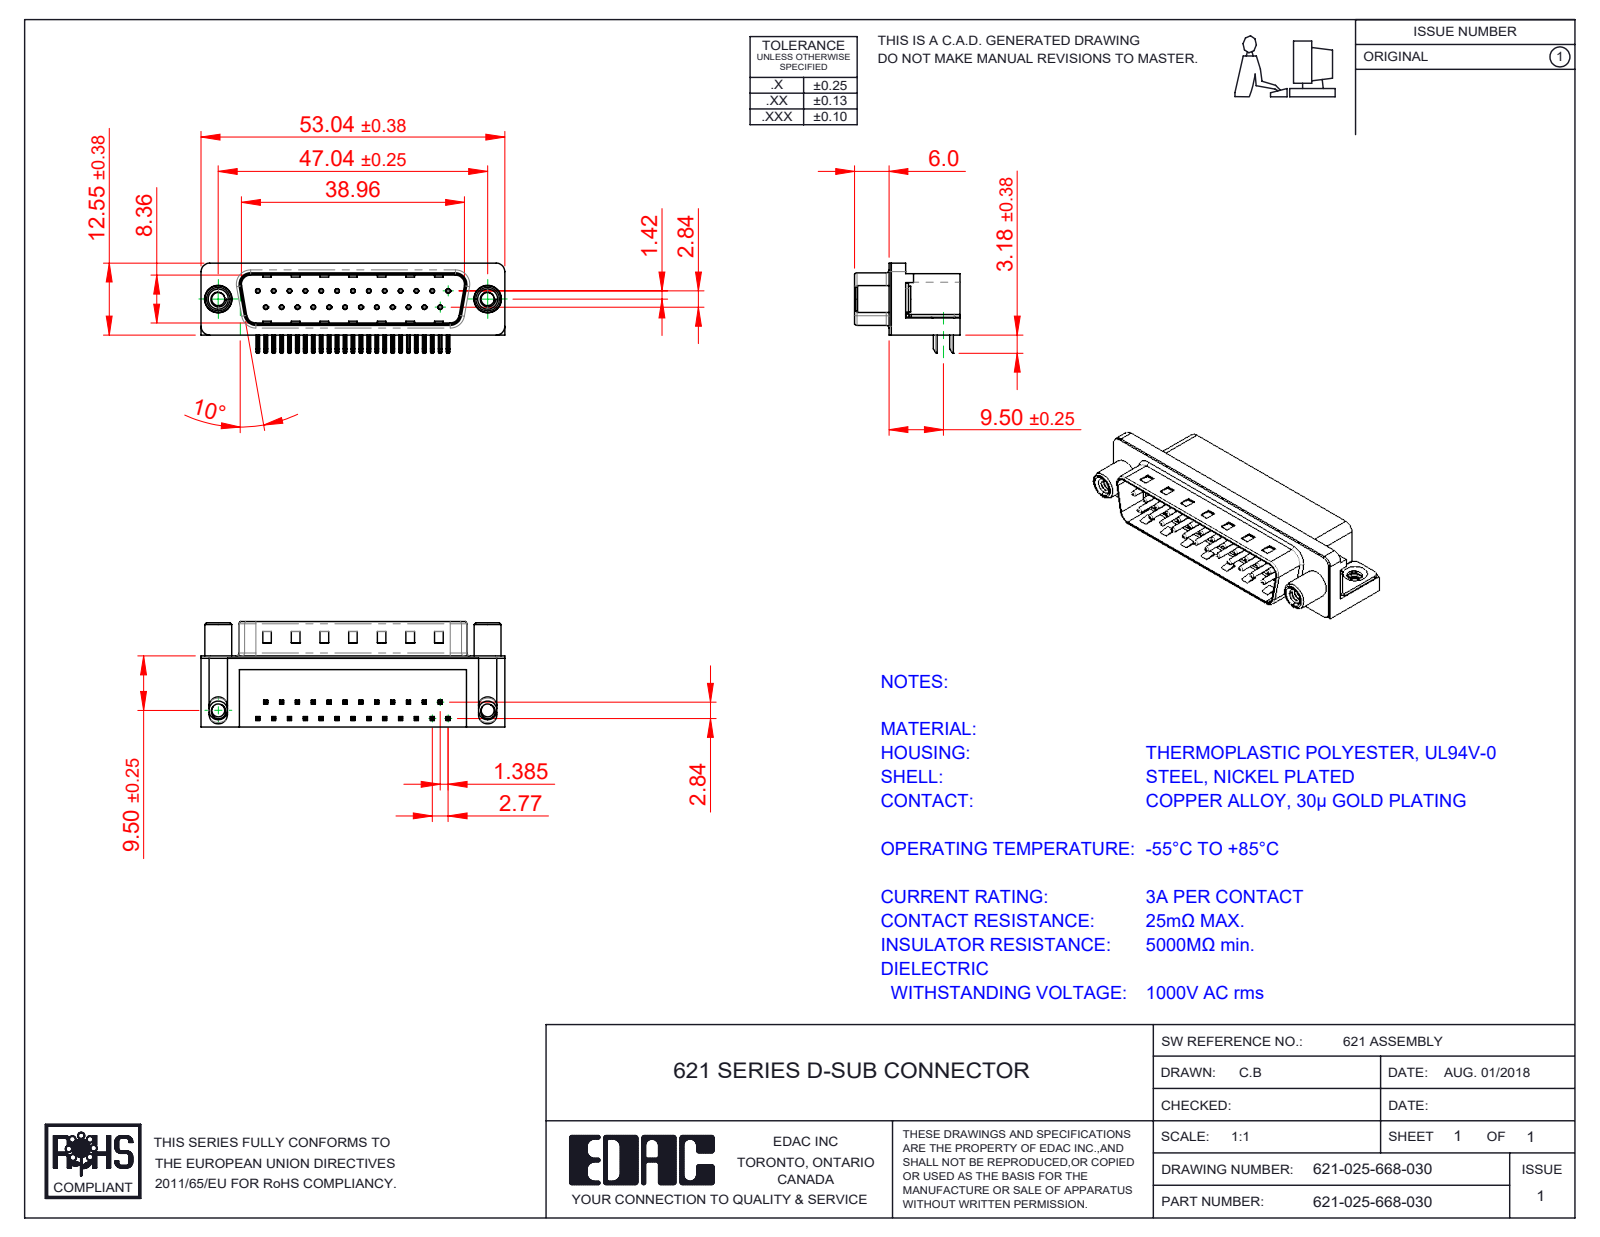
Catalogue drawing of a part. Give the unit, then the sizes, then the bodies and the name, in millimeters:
Units: millimetres
Overall size (bounding box): 53.04 × 18.4 × 16.25
Round holes (diameter × count): ⌀0.35 ×25, ⌀0.8 ×25, ⌀2.3 ×2, ⌀3.1 ×2, ⌀4 ×2, ⌀4.8 ×2, ⌀5 ×2
Round bosses / shafts (diameter × count): ⌀0.75 ×25, ⌀4.9 ×2, ⌀4.7 ×2, ⌀4.5 ×2, ⌀3.85 ×2
Partial cylindrical surfaces — rounded edges, fillets, slot ends (radius × count): R0.25 ×100, R0.12 ×50, R1 ×16, R0.5 ×14, R1.6 ×8, R1.5 ×7, R0.32 ×4, R0.9 ×4
Main face-to-face distances: 0.4, 12, 10.35, 2.1, 8.76, 10.46, 1.7, 10.86, 12.4, 9
Hole centre spacings: 3.16, 2.77, 5.54, 8.31, 11.08, 13.85, 16.62, 5.03
Volume: 6 437 mm³ · Surface area: 7 888 mm²
Bodies: 31 solids, 2297 faces (1429 planar, 675 cylindrical, 193 other)
Part name (STEP PRODUCT): 621 Housing_25 Socket; 621 Contact Top; 621 2 Prong Board Lock; 621 Contact Bottom (+3 more)
STEP written by: SolidWorks 2016 (CONFIG_CONTROL_DESIGN)
